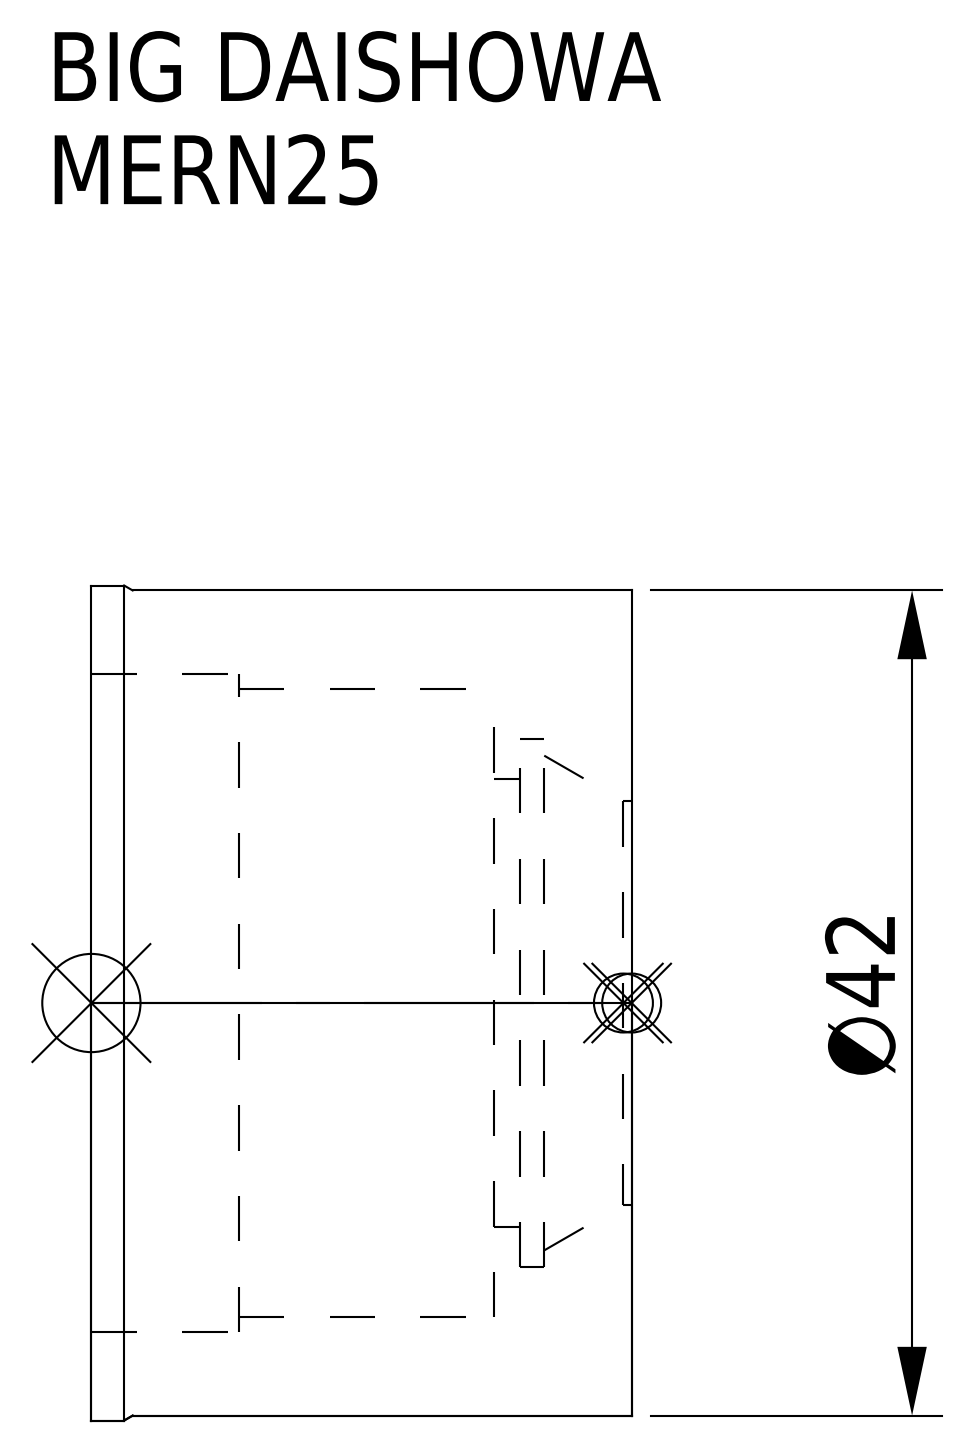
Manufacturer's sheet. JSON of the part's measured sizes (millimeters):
{"part_name": "MERN25", "step_written_by": "CREO PARAMETRIC BY PTC INC, 2016380 (AUTOMOTIVE_DESIGN)", "units": "millimeters", "bodies": {"solids": 1, "faces": 24, "planar": 6, "cylindrical": 14, "other": 4}, "overall_size": [42.5, 42.5, 27.5], "volume_mm3": 18057, "surface_area_mm2": 8592, "round_holes": [[20.53, 1], [22.8, 1], [26.9, 1], [32, 1], [33.5, 1]], "round_bosses_or_shafts": [[42.5, 1], [42, 1]], "face_to_face_distances": [27.5, 7, 20.5, 5.7, 1.3, 21.8, 20, 14.3, 13, 7.5]}
